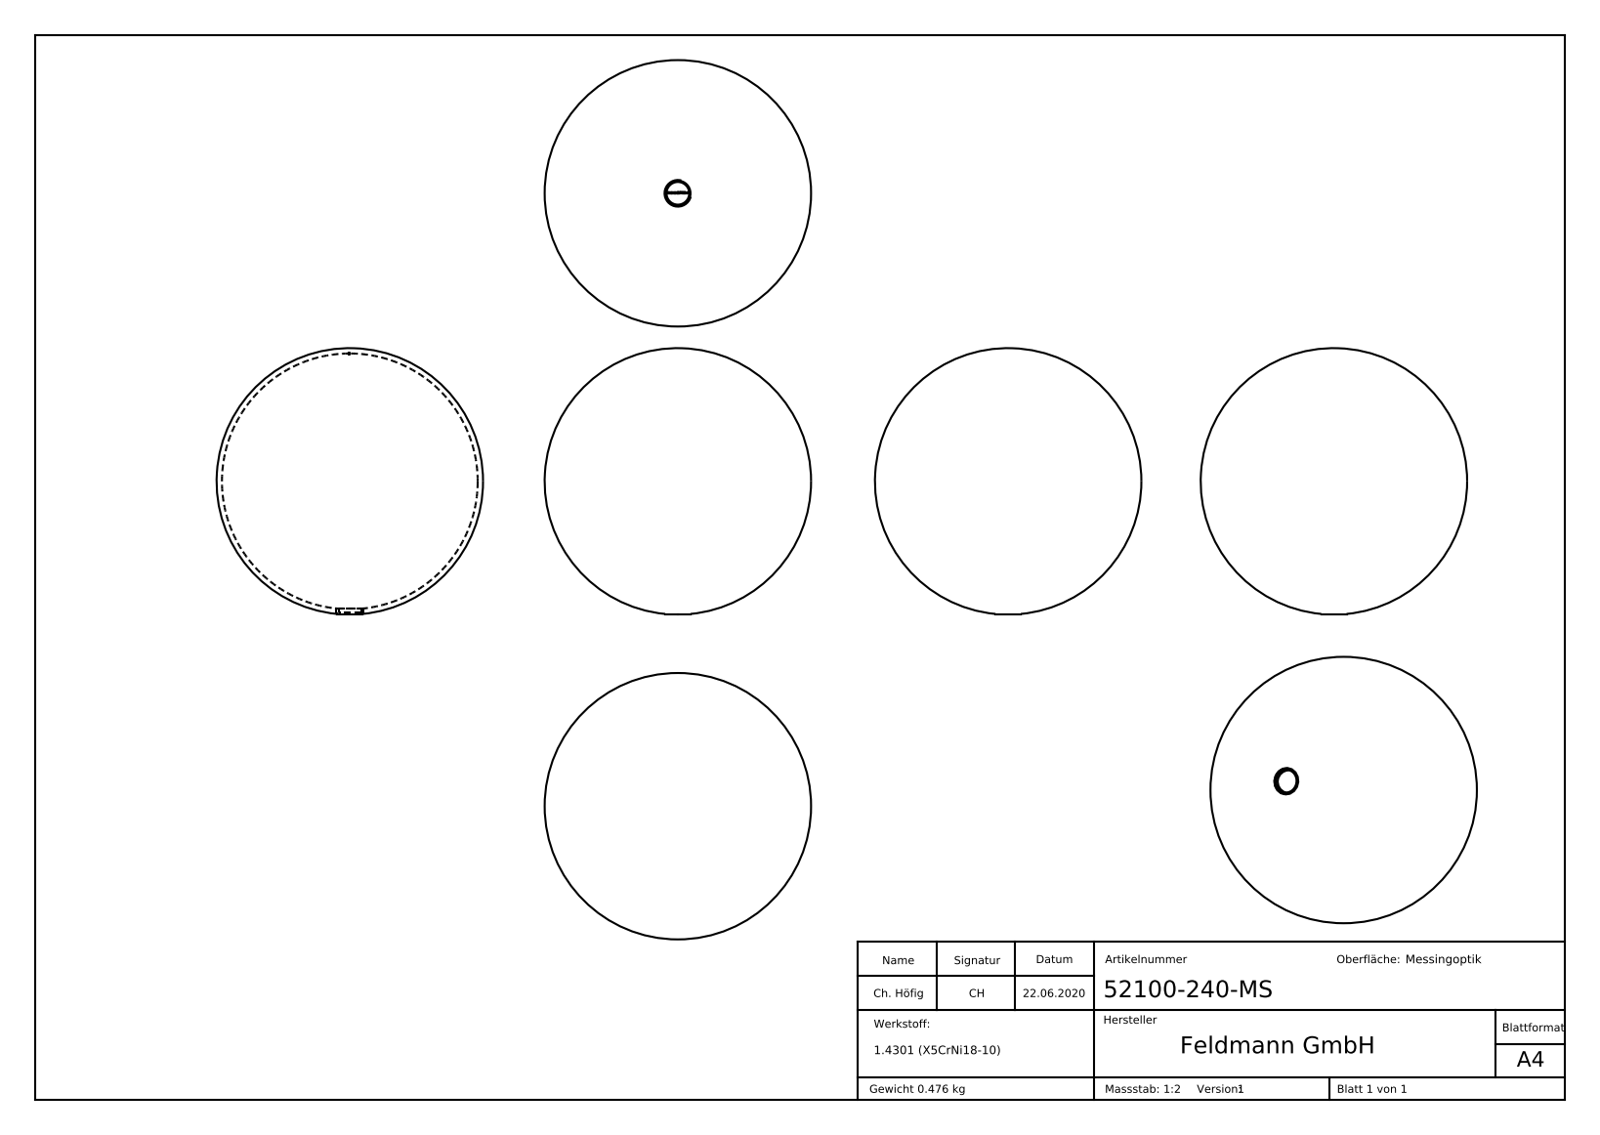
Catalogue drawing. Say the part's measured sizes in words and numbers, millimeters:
The part is named "52100-240-MS". Its 3-D file was written by "SolidWorks 2015 (CONFIG_CONTROL_DESIGN)". It is 1 solid with 255 faces: 114 planar, 1 cylindrical and 140 other. Overall it measures 100 by 100 by 99.77 millimeters. Its volume is 60 235 cubic millimeters and its surface area 60 305 square millimeters. Round holes: 1 of diameter 8.5. The main face-to-face distances are 1.12, 0.45, 0.5, 0.76, 0.33, 1.85, 3.2, 0.62, 1.93, 5.05.
